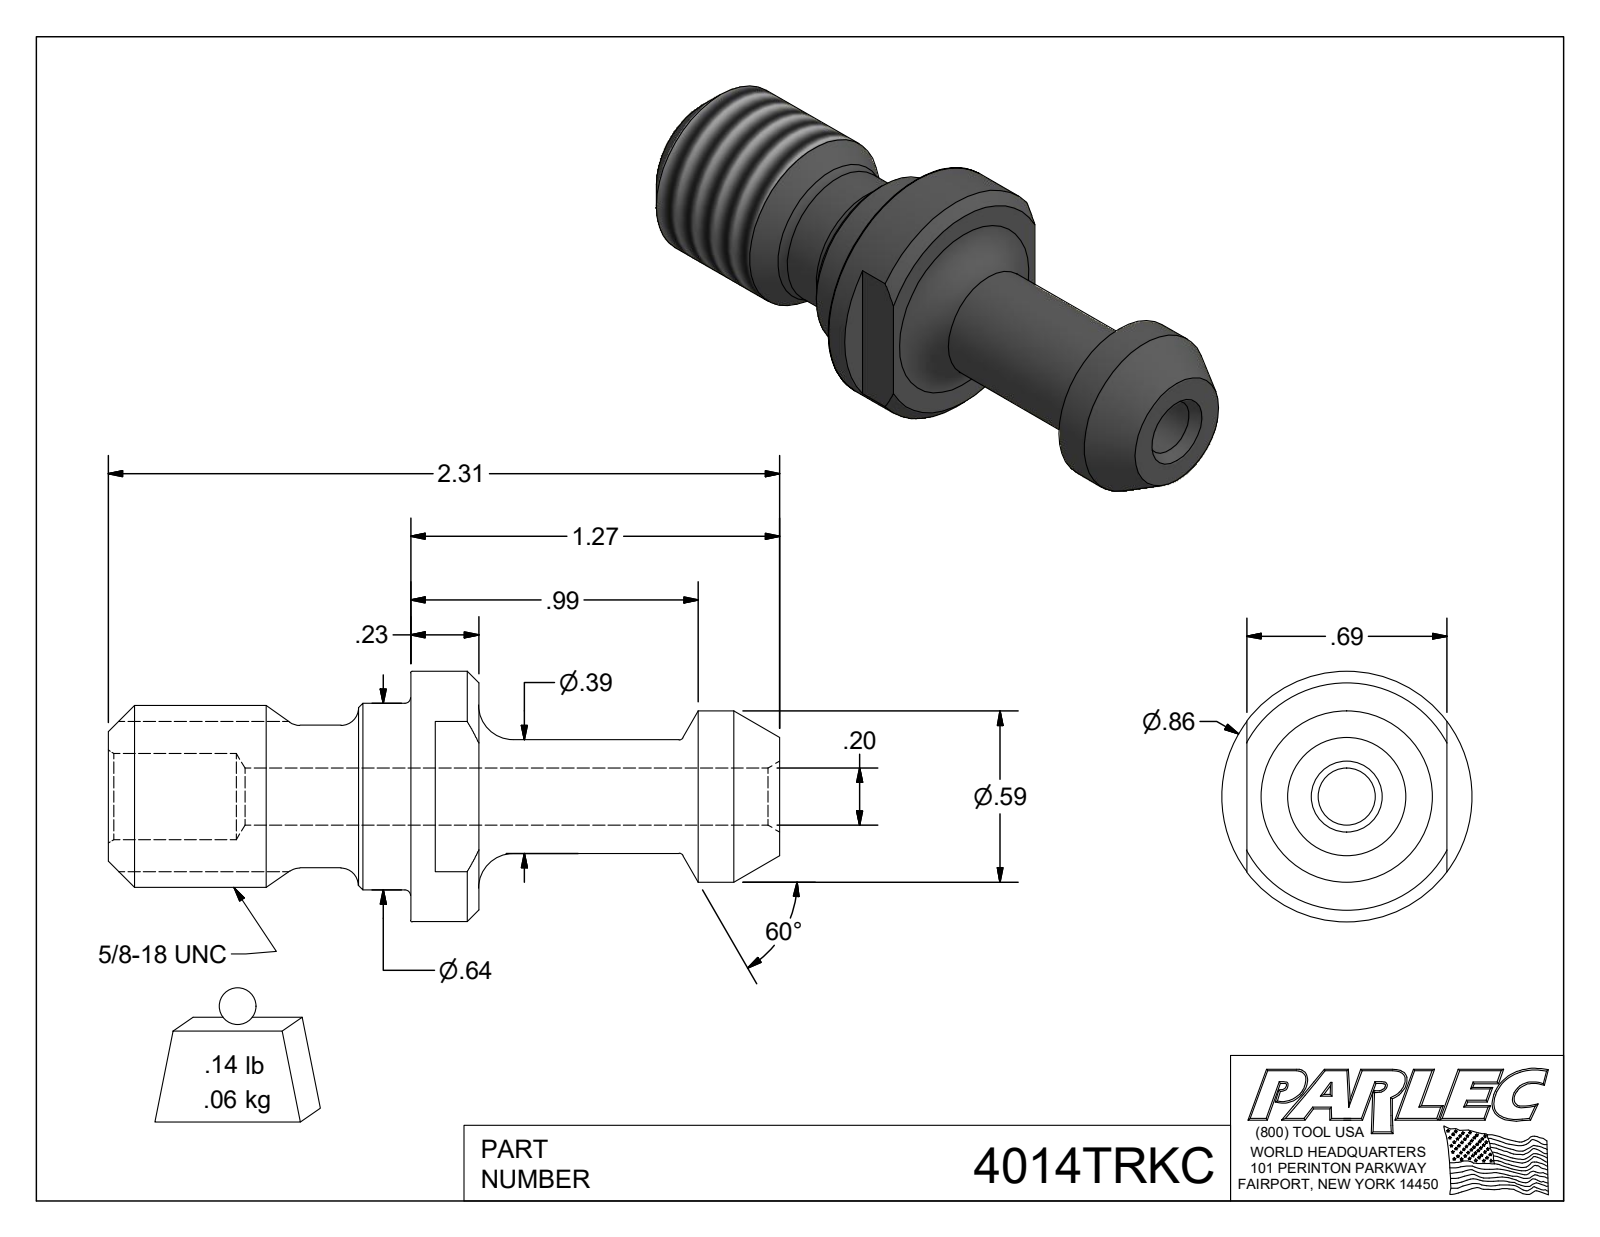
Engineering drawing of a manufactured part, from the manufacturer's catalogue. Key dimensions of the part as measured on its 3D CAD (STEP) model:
Part name (STEP PRODUCT): 4014TRKC
STEP written by: Autodesk Inventor 2018 (AUTOMOTIVE_DESIGN)
Units: inches
Bodies: 1 solid, 37 faces (10 planar, 8 cylindrical, 19 other)
Overall size (bounding box): 2.308 × 0.86 × 0.86
Volume: 0.483 in³ · Surface area: 6.65 in²
Round holes (diameter × count): ⌀0.197 ×1, ⌀0.297 ×1
Round bosses / shafts (diameter × count): ⌀0.86 ×1, ⌀0.64 ×1, ⌀0.625 ×1, ⌀0.588 ×1, ⌀0.49 ×1, ⌀0.391 ×1
Main face-to-face distances: 0.234, 1.268, 1.034, 0.688, 0.084, 0.15, 1.184, 1.04, 1.124, 1.274
